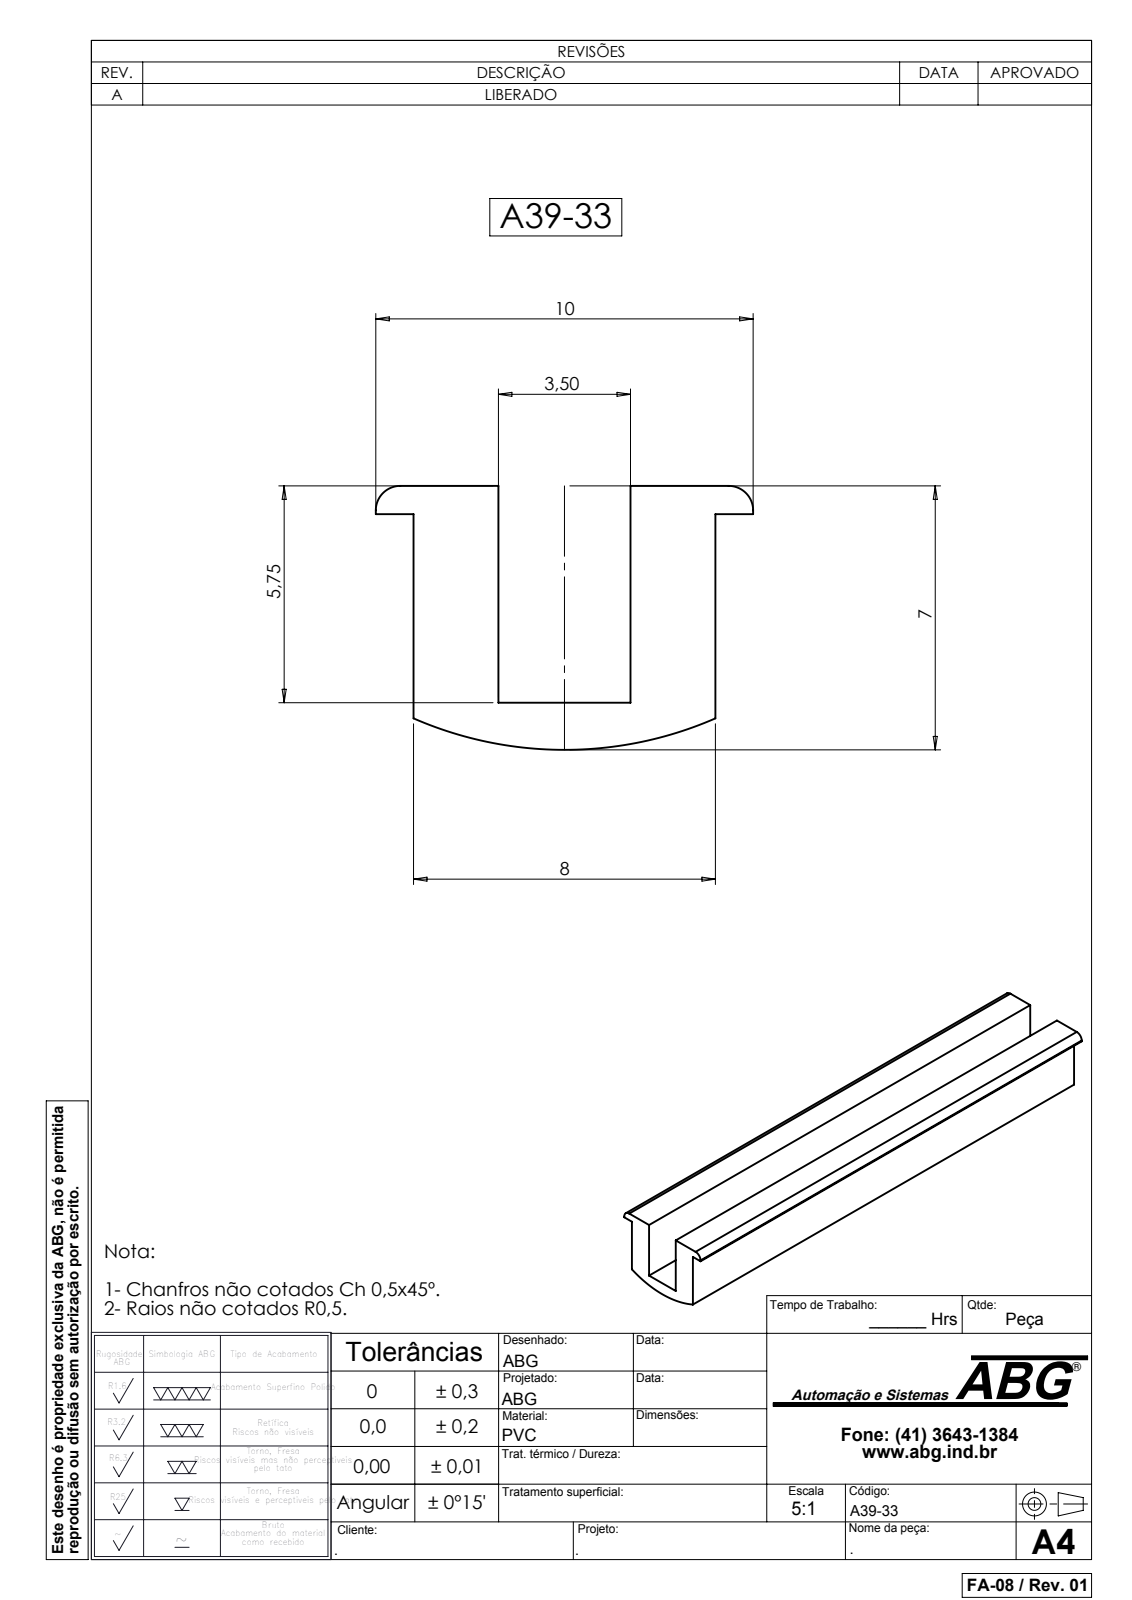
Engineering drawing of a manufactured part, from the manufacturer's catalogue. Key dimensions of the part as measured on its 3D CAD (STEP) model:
Part name (STEP PRODUCT): A39-33
STEP written by: SolidWorks 2007 (CONFIG_CONTROL_DESIGN)
Units: millimetres
Bodies: 1 solid, 16 faces (13 planar, 3 cylindrical, 0 other)
Overall size (bounding box): 50 × 10 × 7
Volume: 1 750 mm³ · Surface area: 2 245 mm²
Partial cylindrical surfaces — rounded edges, fillets, slot ends (radius × count): R0.65 ×2, R10 ×1
Main face-to-face distances: 5.75, 2.25, 3.5, 8, 5, 0.75, 50, 1, 3.25, 6.75
